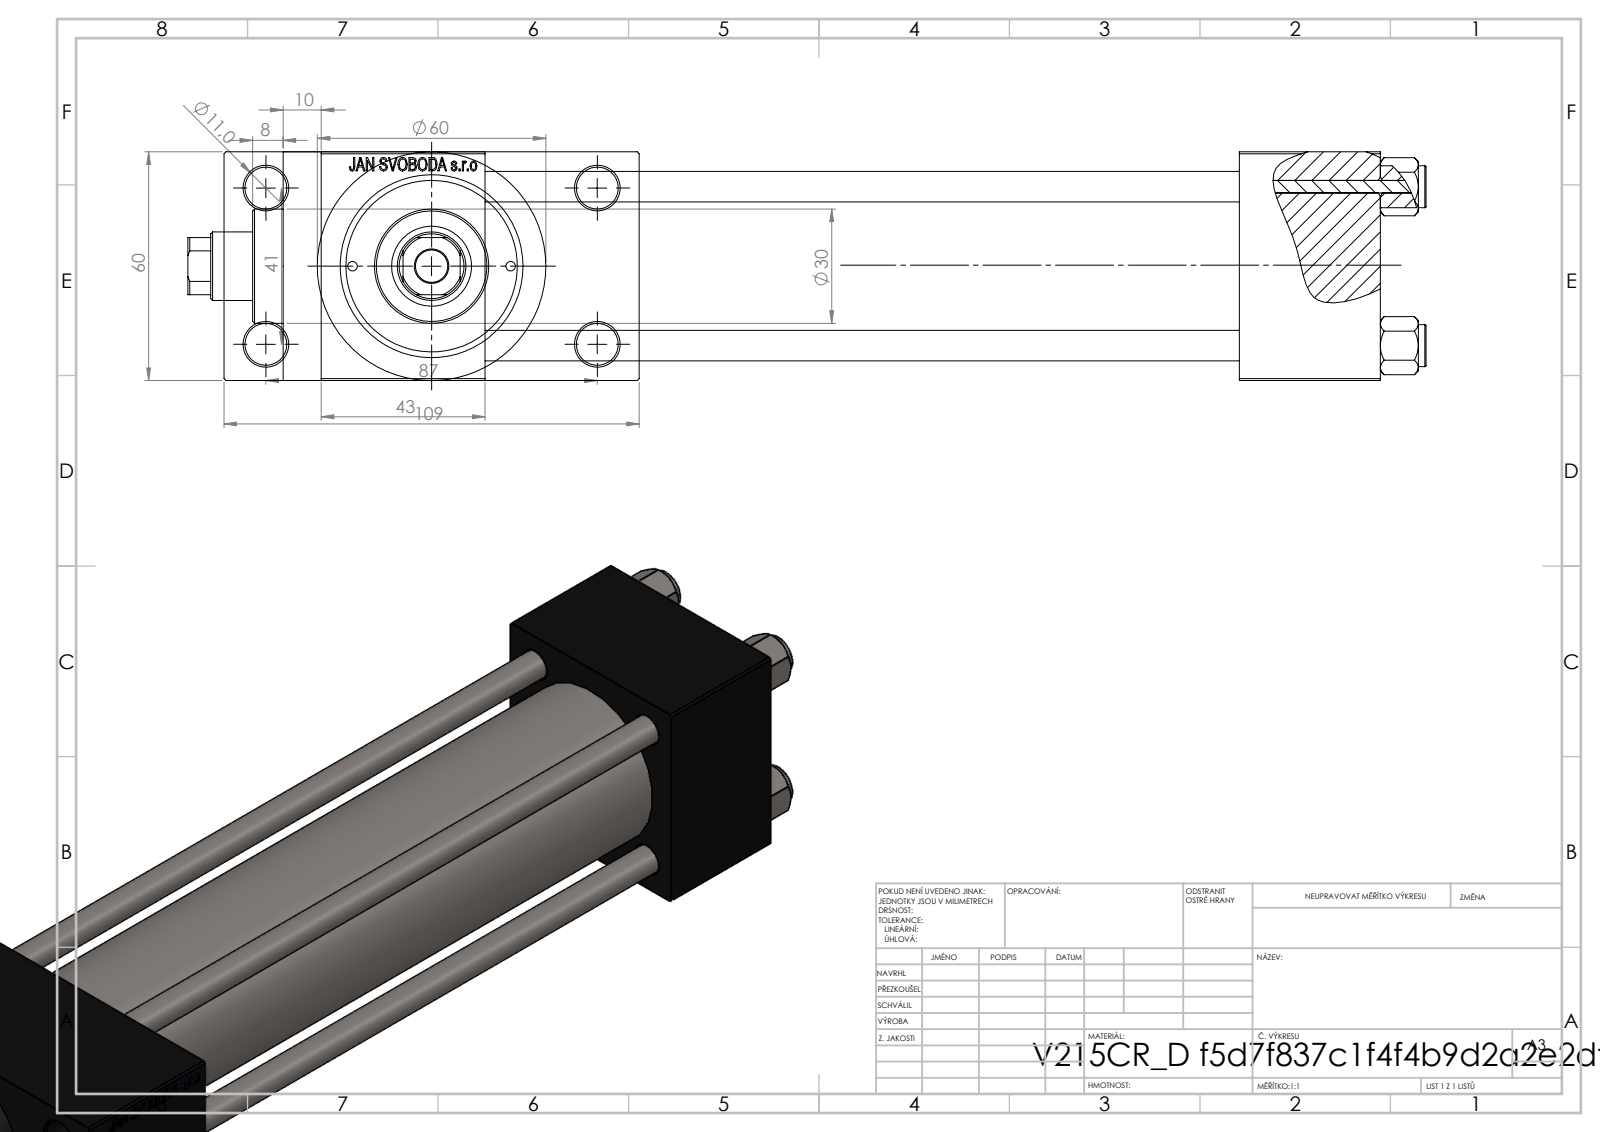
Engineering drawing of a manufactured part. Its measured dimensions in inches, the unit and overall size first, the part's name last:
Units: inches
Overall size (bounding box): 12.795 × 4.291 × 2.362
Round holes (diameter × count): ⌀0.315 ×4, ⌀0.433 ×4, ⌀0.098 ×2, ⌀0.276 ×2, ⌀0.656 ×2, ⌀0.945 ×2, ⌀0.335 ×1, ⌀0.709 ×1, ⌀0.827 ×1, ⌀1.22 ×1, ⌀1.575 ×1, ⌀1.772 ×1
Round bosses / shafts (diameter × count): ⌀0.433 ×4, ⌀2.362 ×1, ⌀1.811 ×1, ⌀1.181 ×1
Partial cylindrical surfaces — rounded edges, fillets, slot ends (radius × count): R0.335 ×1
Main face-to-face distances: 2.362, 7.795, 0.965, 3.327, 1.457, 9.252, 10.945, 9.488, 1.693, 9.635
Hole centre spacings: 0.821, 0.892, 1.161, 1.206, 1.642, 1.832, 1.856, 1.893
Volume: 38.62 in³ · Surface area: 282.6 in²
Bodies: 11 solids, 1112 faces (500 planar, 92 cylindrical, 520 other)
Part name (STEP PRODUCT): V215_VC_A; V215CR_D_Body; NUT_M5_D; V215CR_VCP_D (+1 more)
STEP written by: SolidWorks 2019 (CONFIG_CONTROL_DESIGN)
